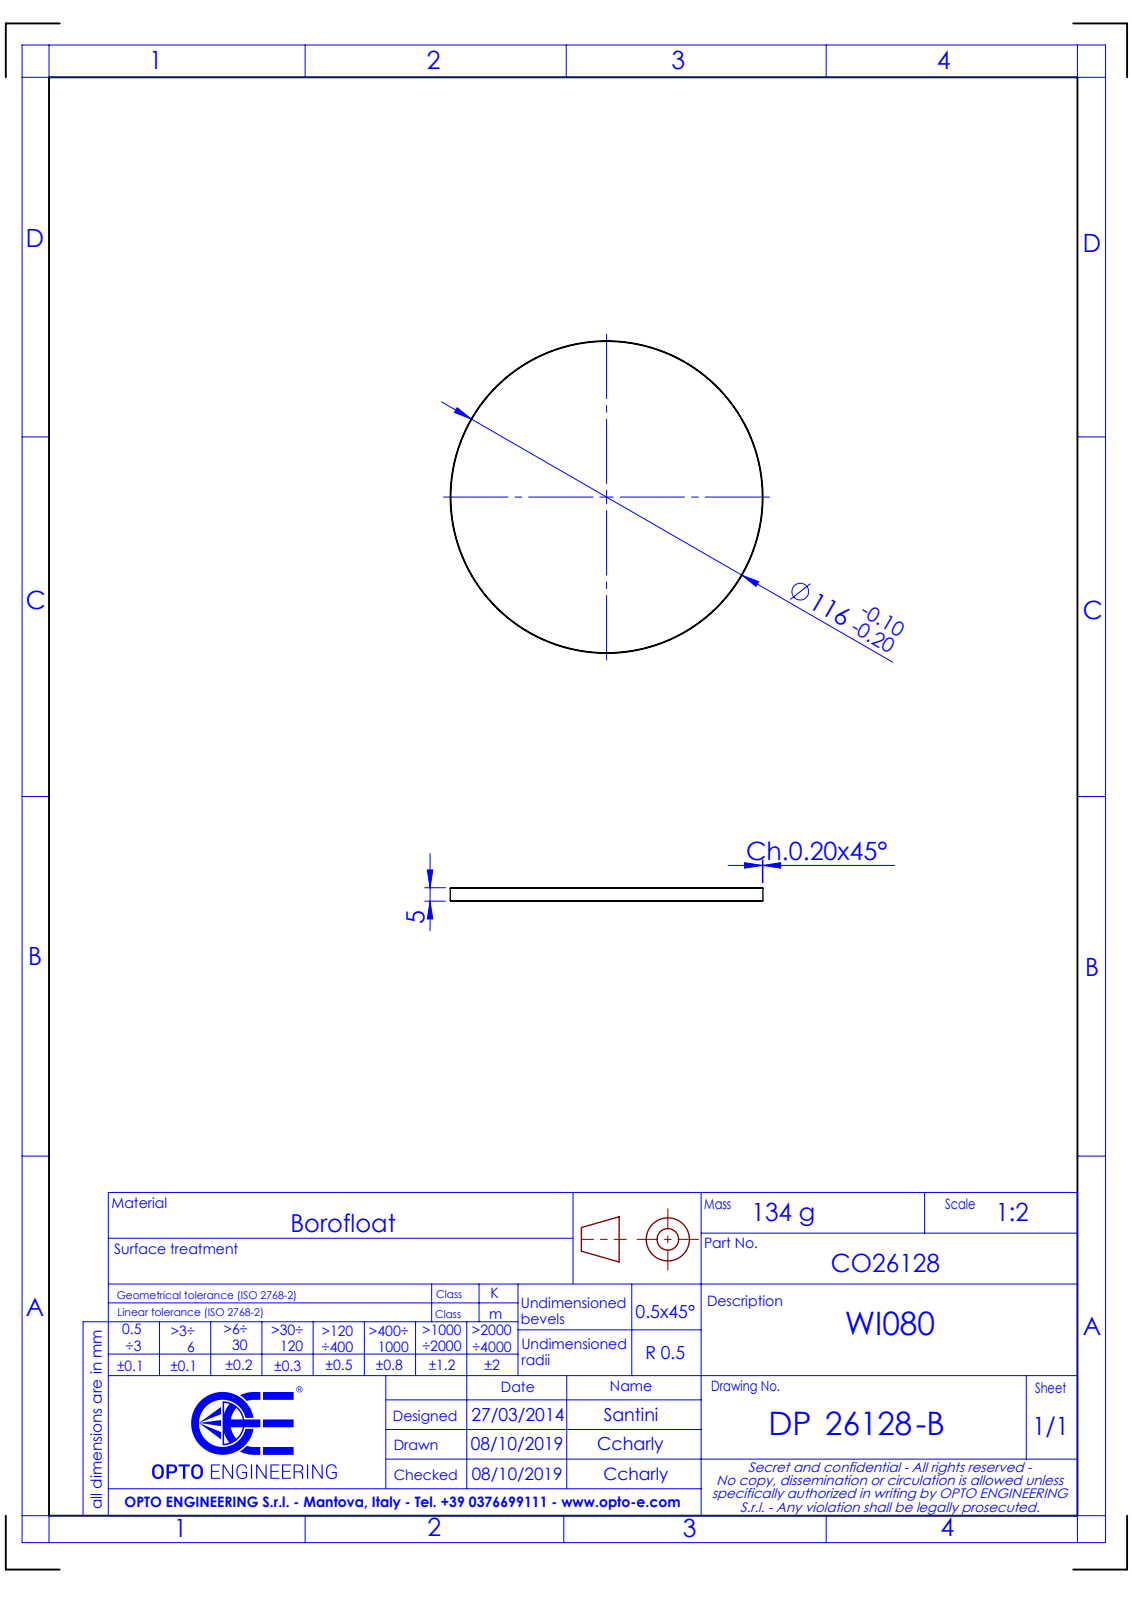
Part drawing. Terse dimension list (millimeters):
name: DP26128_WI080
written by: SolidWorks 2021 (CONFIG_CONTROL_DESIGN)
unit: mm
bodies: 1 solid, 8 faces (2 planar, 2 cylindrical, 4 other)
size: 116 × 116 × 5
volume: 52 827 mm³; area: 22 873 mm²
bosses: 1× ⌀116
face distances: 5
